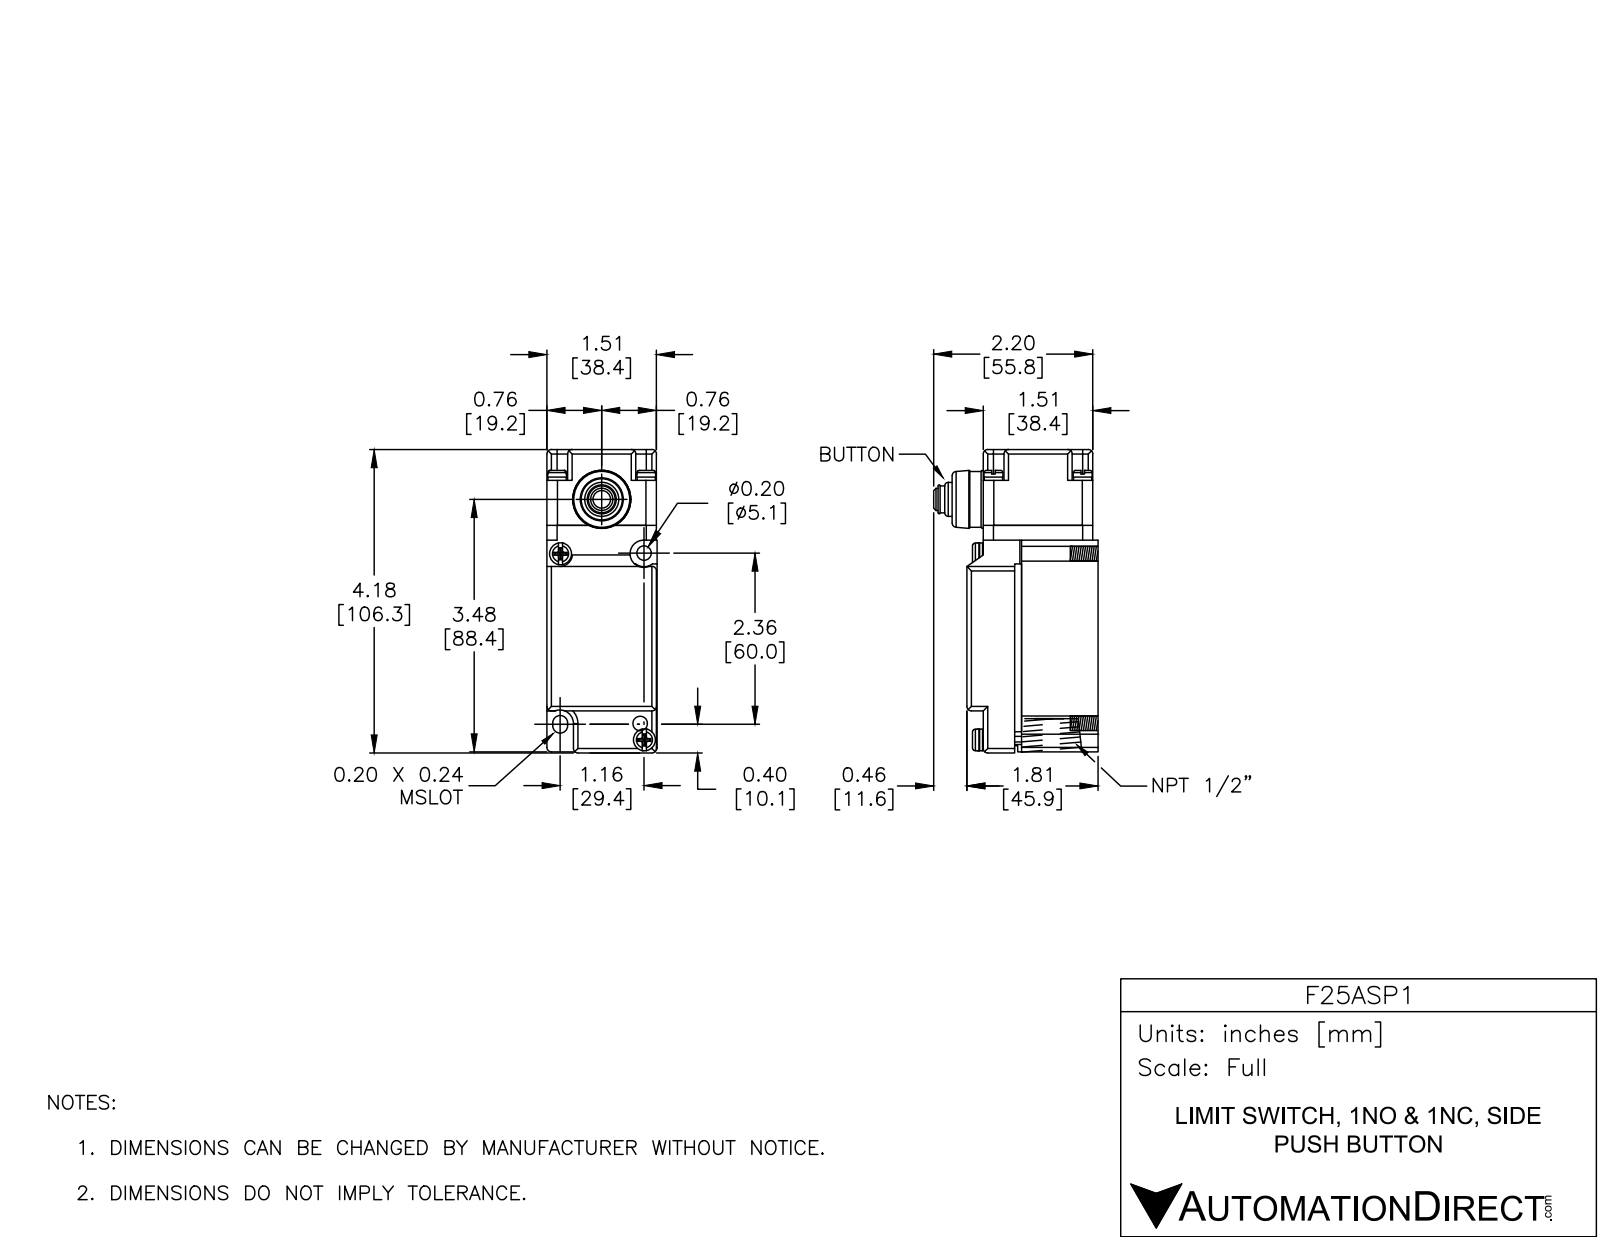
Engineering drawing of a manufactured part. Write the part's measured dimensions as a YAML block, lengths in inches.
part_name: "F25ASP1; Imported1; Imported; Imported5 (+8 more)"
step_written_by: "SolidWorks 2002296 (CONFIG_CONTROL_DESIGN)"
units: inches
bodies: {solids: 12, faces: 636, planar: 241, cylindrical: 182, other: 213}
overall_size: [4.184, 2.267, 1.52]
volume: 10.18
surface_area: 71.07
round_holes:
  - {diameter: 0.177, count: 4}
  - {diameter: 0.19, count: 3}
  - {diameter: 0.2, count: 3}
  - {diameter: 0.08, count: 1}
  - {diameter: 0.204, count: 1}
  - {diameter: 0.23, count: 1}
  - {diameter: 0.232, count: 1}
  - {diameter: 0.26, count: 1}
  - {diameter: 0.419, count: 1}
  - {diameter: 0.58, count: 1}
  - {diameter: 0.63, count: 1}
  - {diameter: 0.72, count: 1}
round_bosses_or_shafts:
  - {diameter: 0.26, count: 4}
  - {diameter: 0.25, count: 4}
  - {diameter: 0.14, count: 4}
  - {diameter: 0.302, count: 2}
  - {diameter: 0.3, count: 2}
  - {diameter: 0.77, count: 1}
  - {diameter: 0.655, count: 1}
  - {diameter: 0.565, count: 1}
partial_cylinders:
  - {radius: 0.062, count: 29}
  - {radius: 0.03, count: 16}
  - {radius: 0.015, count: 8}
  - {radius: 0.145, count: 8}
  - {radius: 0.14, count: 4}
  - {radius: 0.102, count: 2}
  - {radius: 0.188, count: 2}
  - {radius: 0.19, count: 2}
face_to_face_distances: [0.094, 1.149, 1.055, 1.52, 0.66, 0.754, 1.809, 1.51, 0.227, 0.433]
hole_center_spacings: [1.23, 1.23, 1.74, 2.815, 0.225, 0.235, 0.755, 0.755]
